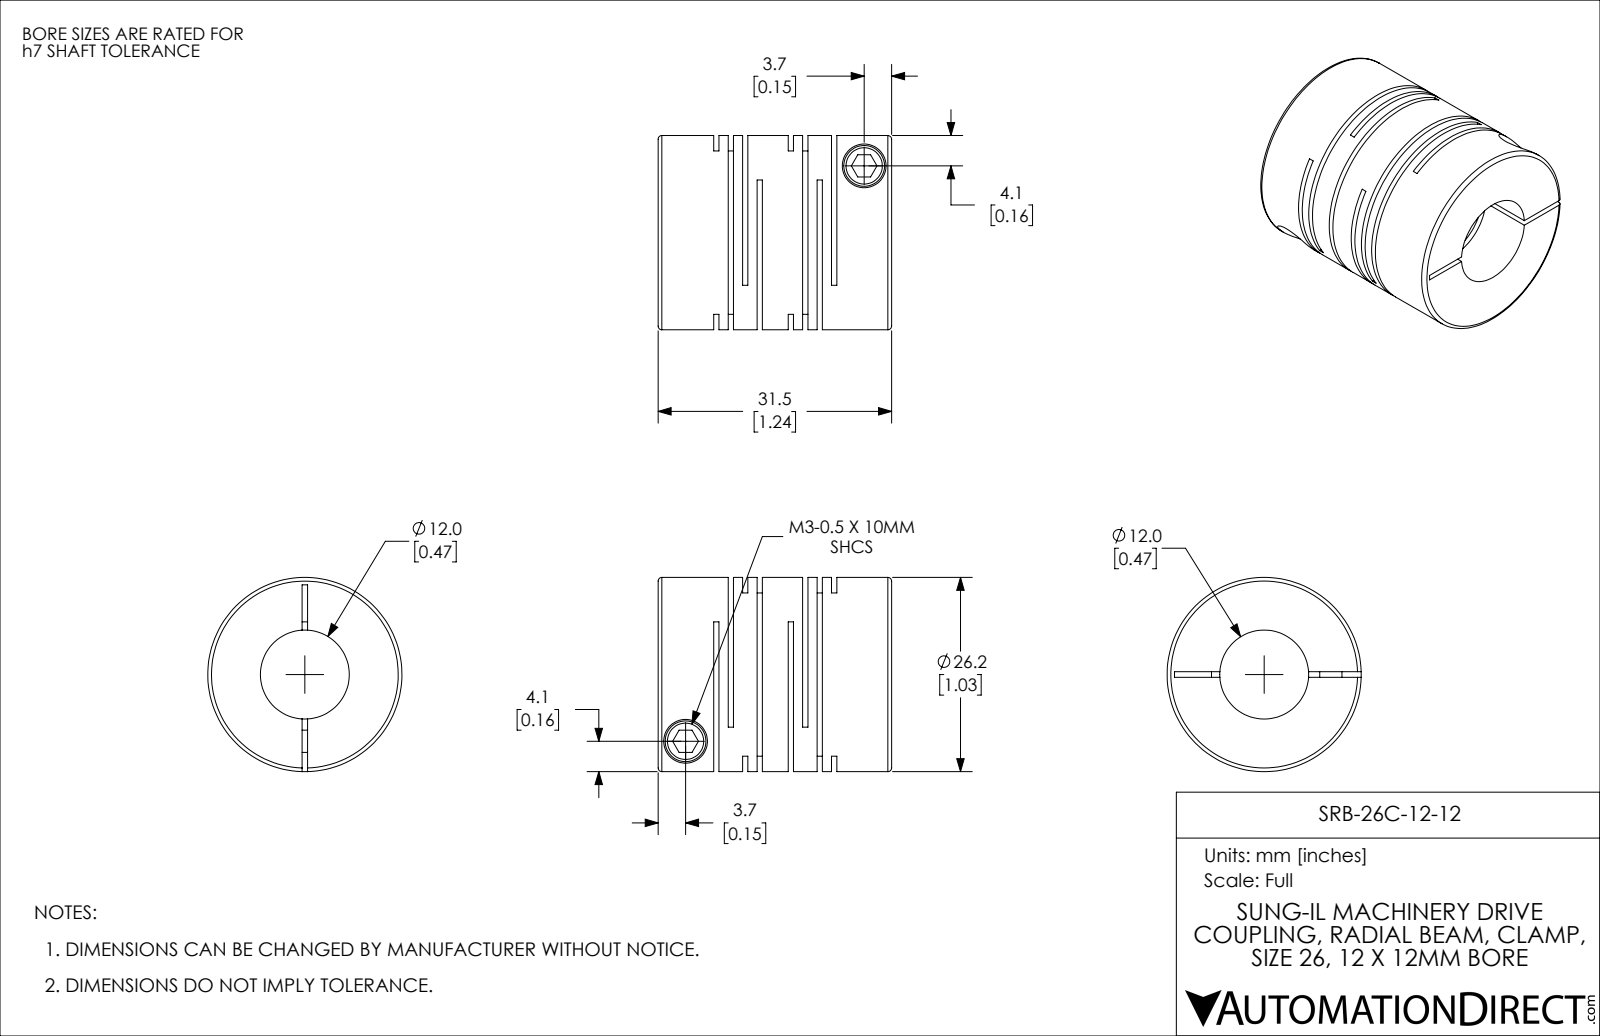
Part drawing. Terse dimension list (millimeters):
name: SRB-26C-12-12
written by: SolidWorks 2021 (CONFIG_CONTROL_DESIGN)
unit: mm
bodies: 1 solid, 114 faces (60 planar, 42 cylindrical, 12 other)
size: 31.5 × 26.2 × 26.2
volume: 11 073 mm³; area: 10 212 mm²
holes: 2× ⌀3, 2× ⌀5.9, 1× ⌀12
bosses: 2× ⌀5.5, 1× ⌀26.2
face distances: 1.95, 10.05, 0.71, 3.9, 8.1, 12, 1.24, 2.66, 9.34, 13.95
